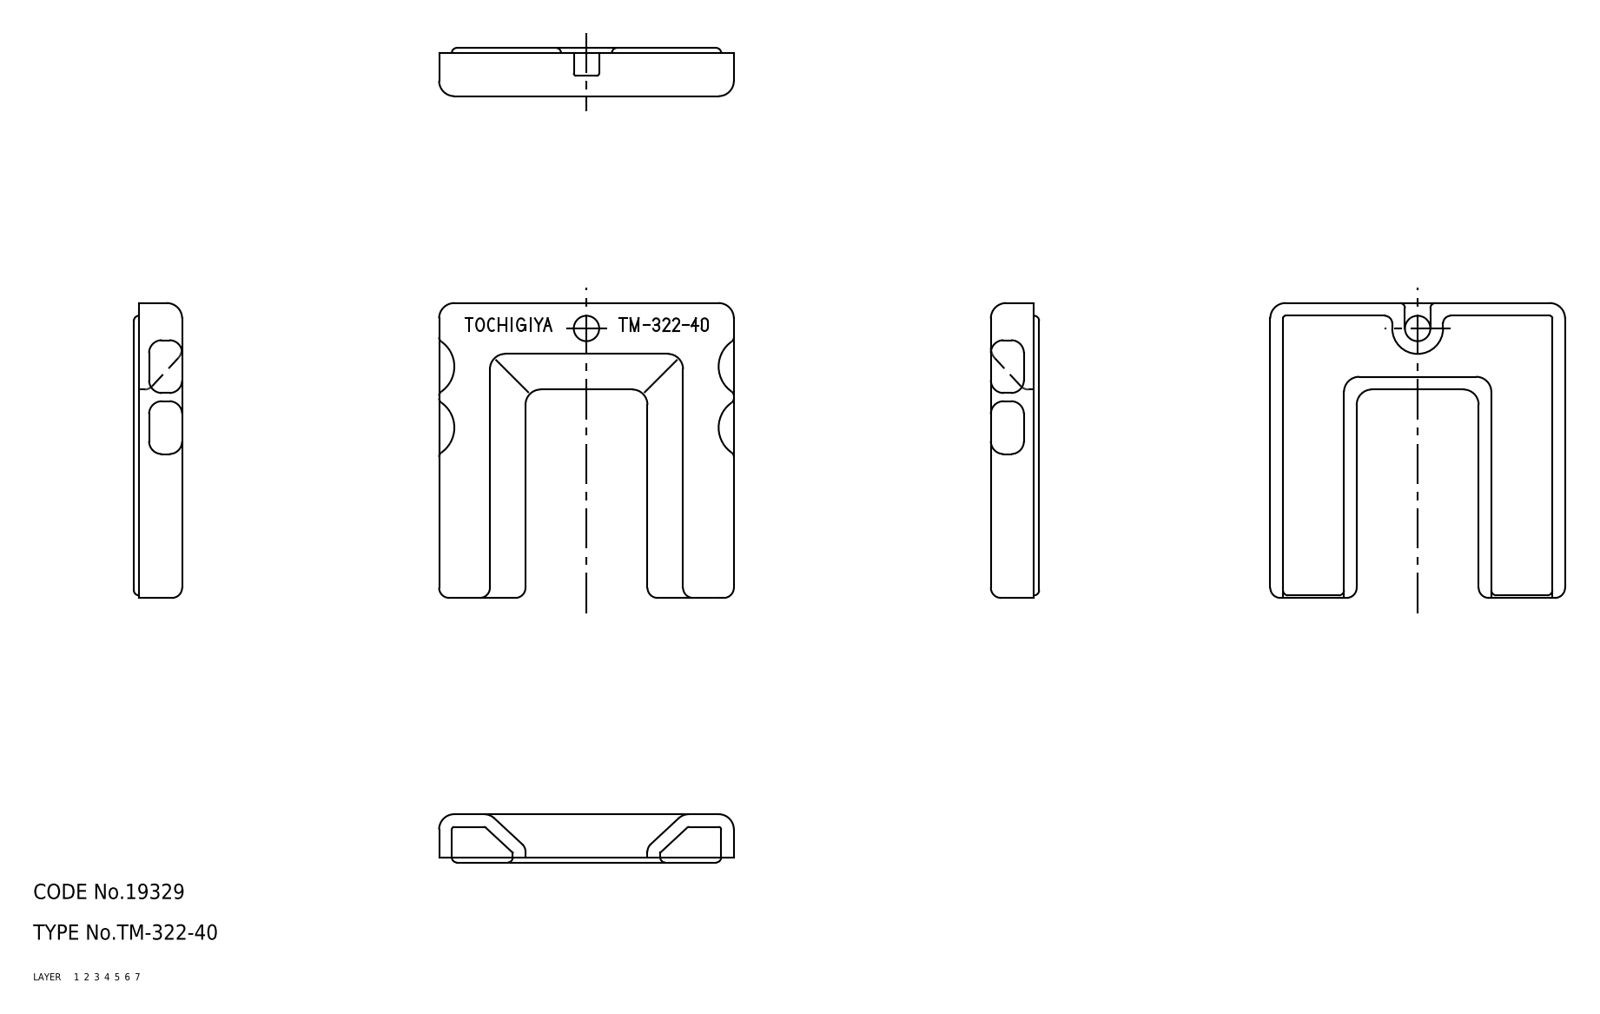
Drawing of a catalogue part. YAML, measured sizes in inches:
part_name: "67121822; 67121835; 67121848"
step_written_by: "CADfix (AUTOMOTIVE_DESIGN)"
units: inches
bodies: {solids: 1, faces: 187, planar: 0, cylindrical: 0, other: 187}
overall_size: [2.283, 2.283, 0.669]
volume: 0.108
surface_area: 16.19
